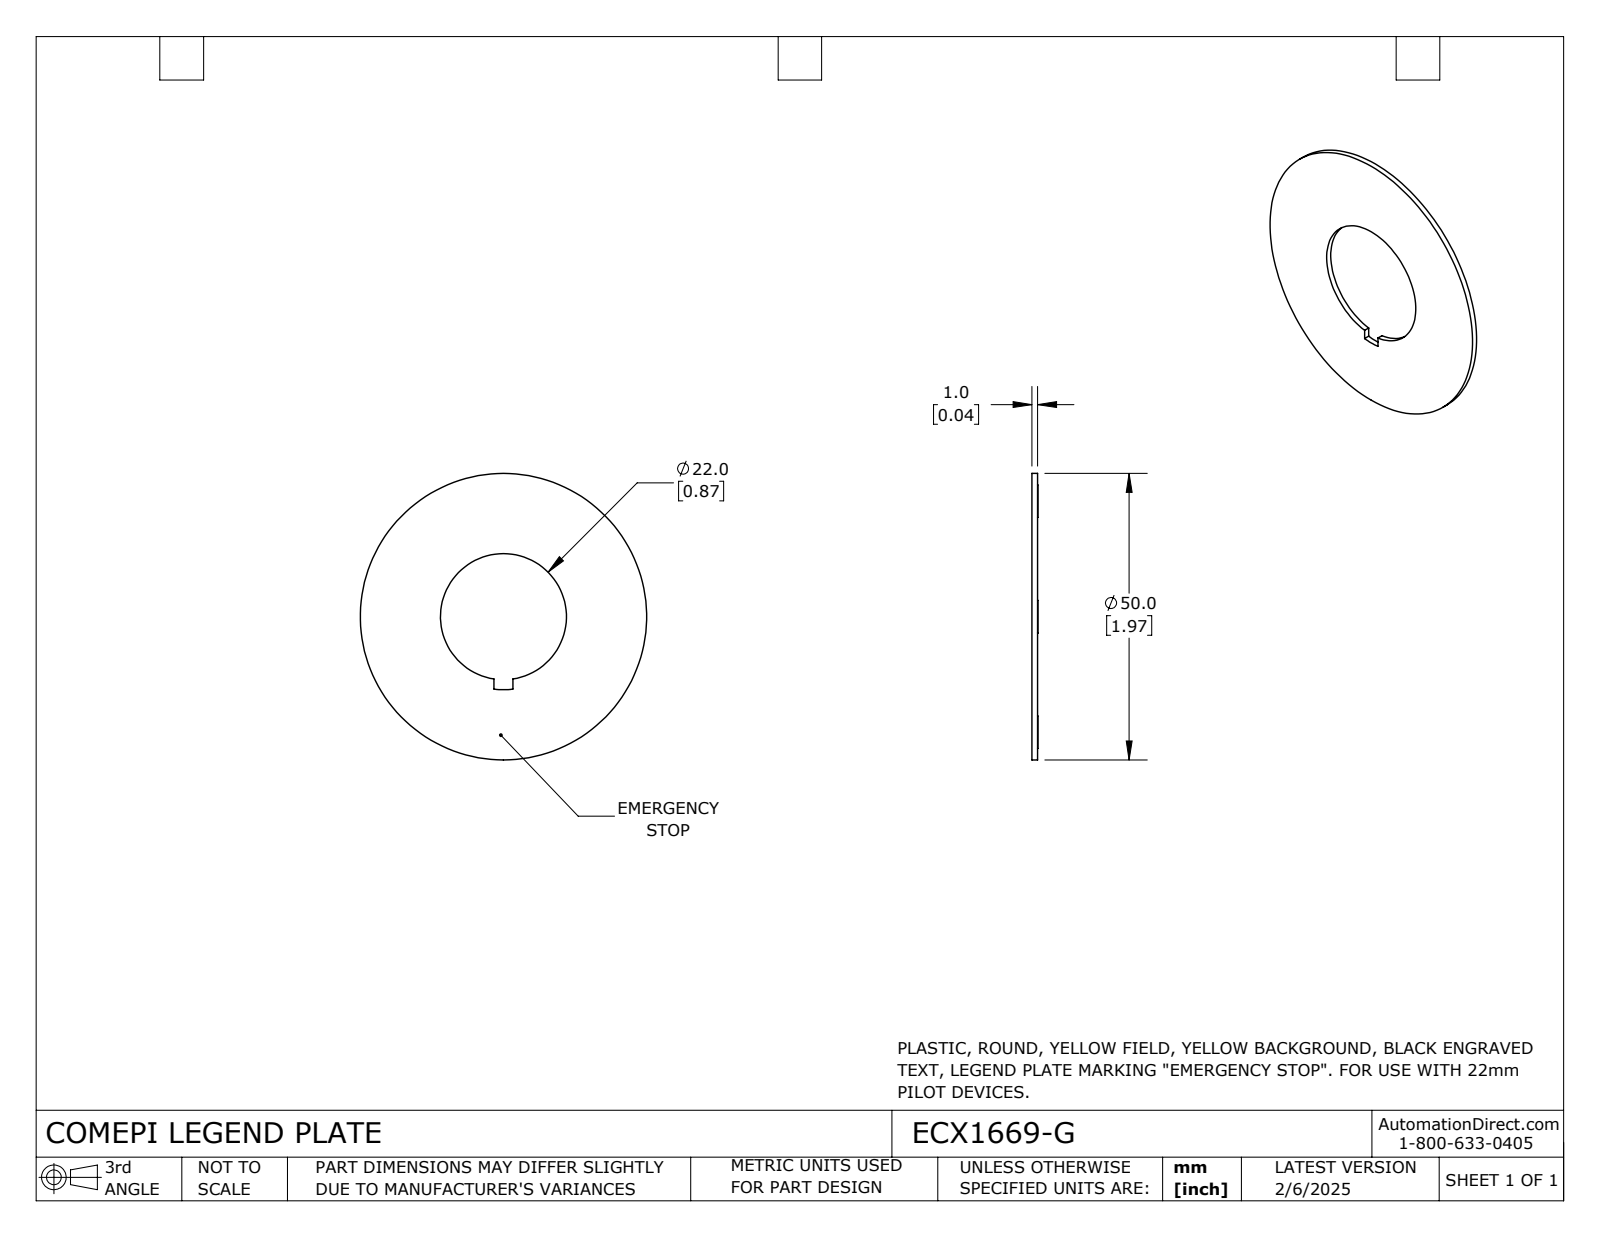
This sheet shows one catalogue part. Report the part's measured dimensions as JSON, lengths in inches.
{"part_name": "ECX1669-G", "step_written_by": "SolidWorks 2024 (CONFIG_CONTROL_DESIGN)", "units": "inches", "bodies": {"solids": 1, "faces": 169, "planar": 68, "cylindrical": 29, "other": 72}, "overall_size": [1.969, 1.969, 0.04], "volume_in3": 0.096, "surface_area_in2": 5.25, "round_holes": [[0.194, 4], [0.866, 1]], "round_bosses_or_shafts": [[0.224, 4], [0.018, 4], [1.969, 1]], "partial_cylinders_radius": [[0.502, 1]], "face_to_face_distances": [0.039, 0.04, 0.13, 0.703, 1.676, 0.694, 0.713, 0.768, 0.898, 0.778], "hole_center_spacings": [0.794, 1.122, 1.587]}
